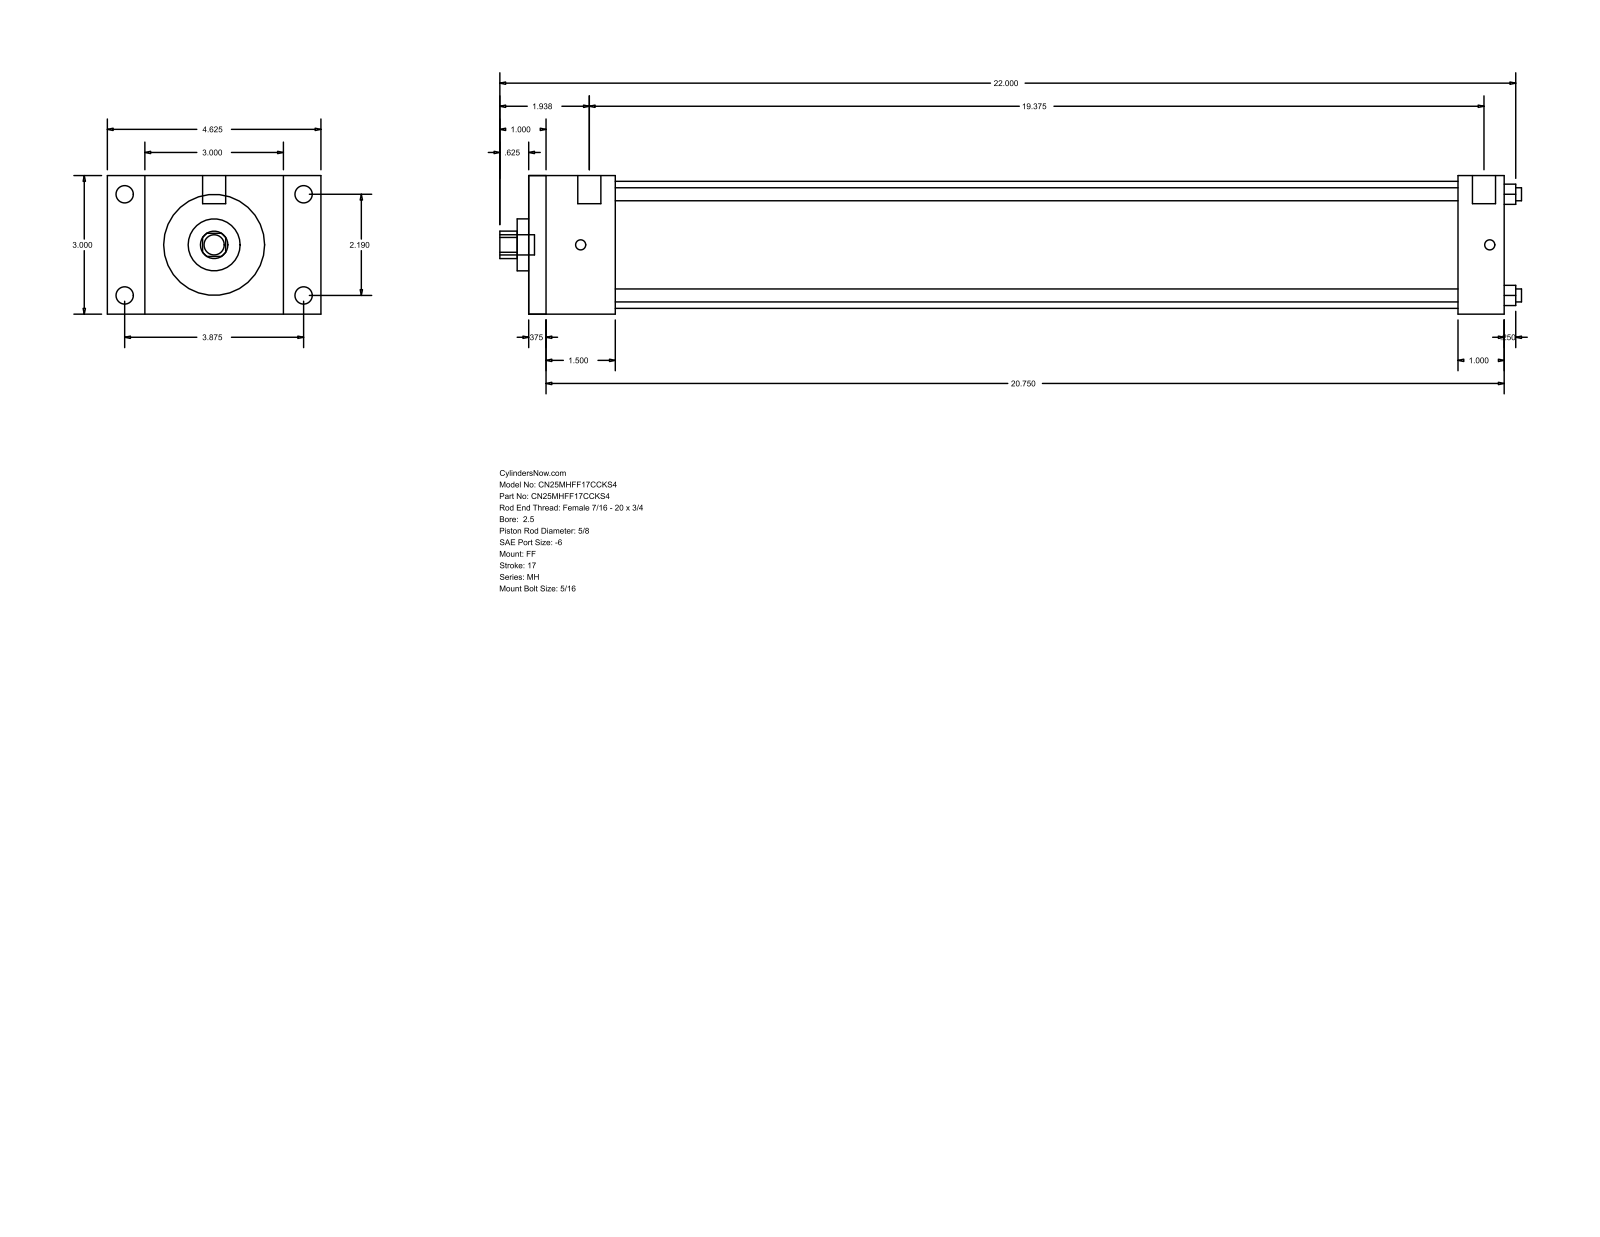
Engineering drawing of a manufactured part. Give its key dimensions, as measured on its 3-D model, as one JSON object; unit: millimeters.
{"part_name": "MH_FF__0250_0.625", "step_written_by": "GSSL Pune (CONFIG_CONTROL_DESIGN)", "units": "millimeters", "bodies": {"solids": 0, "faces": 92, "planar": 64, "cylindrical": 28, "other": 0}, "overall_size": [561.98, 117.47, 76.2], "round_holes": [[7.14, 4], [15.88, 1], [28.57, 1], [69.85, 1]], "round_bosses_or_shafts": [[9.53, 4], [5.56, 4], [12.7, 2], [11.11, 1]], "partial_cylinders_radius": [[7.54, 1]], "face_to_face_distances": [76.2, 536.57, 9.52, 527.05, 25.4, 47.62, 511.17, 38.1, 501.65, 463.55], "hole_center_spacings": [39.33, 55.62, 78.66]}
